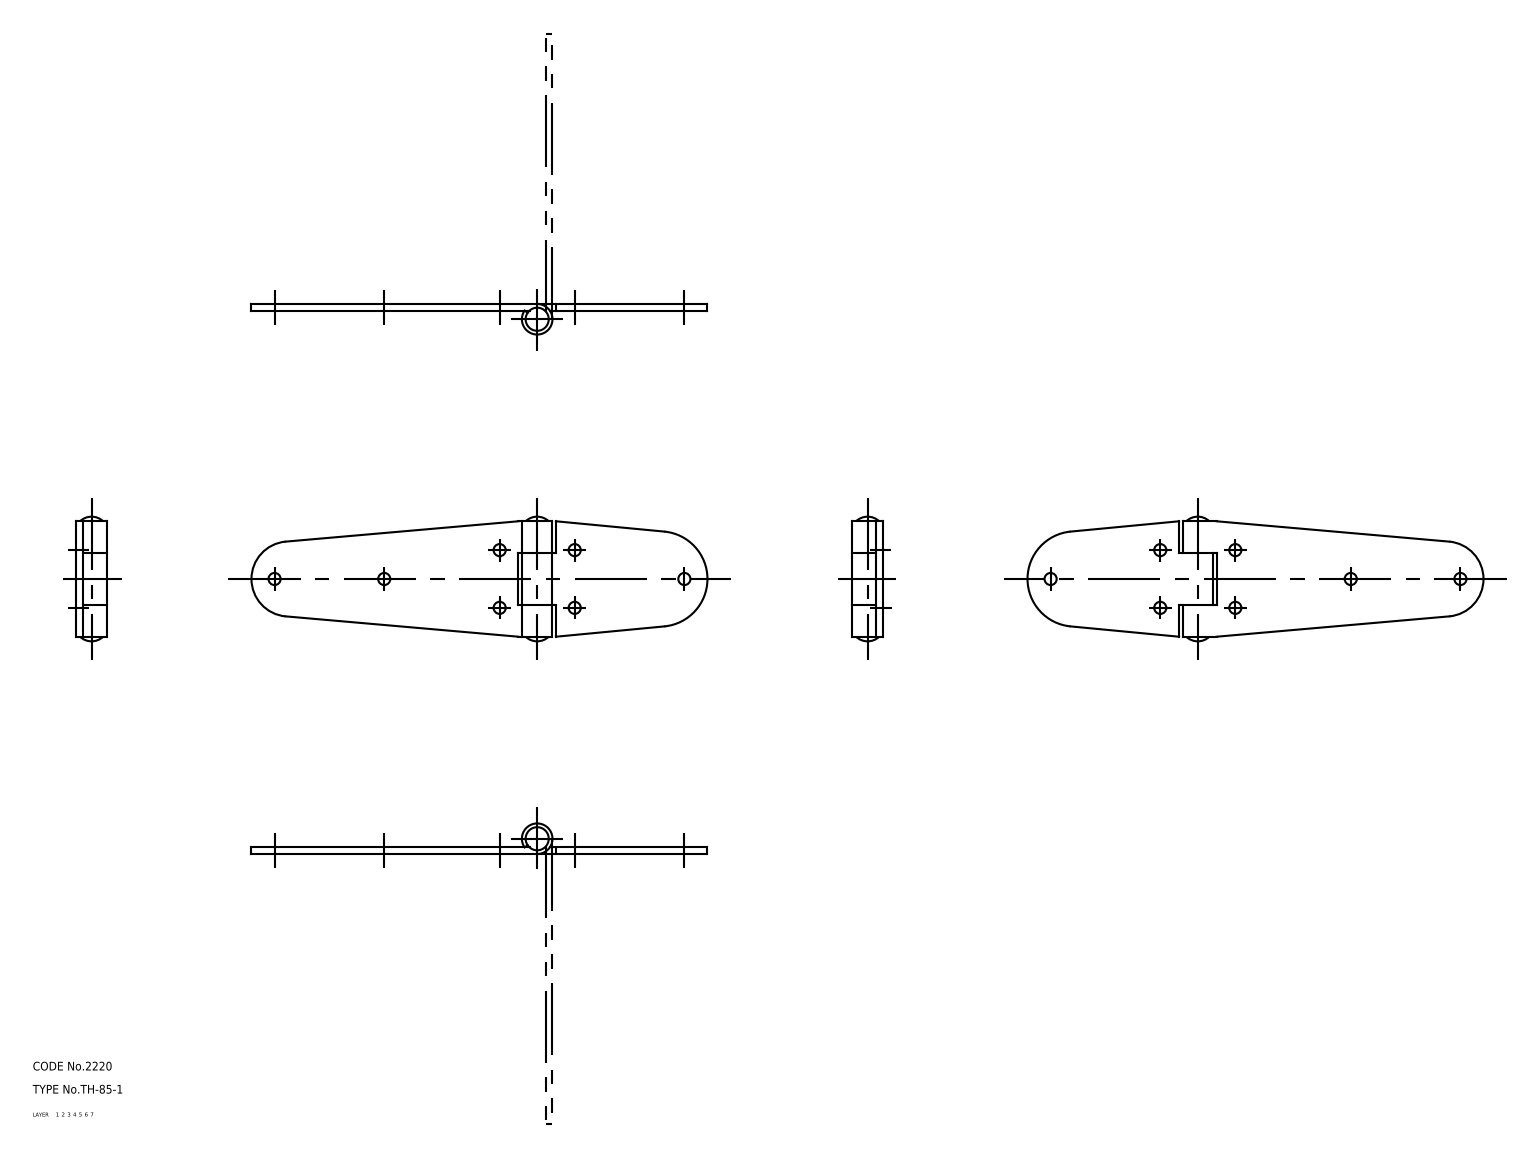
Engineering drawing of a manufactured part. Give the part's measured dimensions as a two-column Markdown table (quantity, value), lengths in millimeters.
| quantity | value |
| --- | --- |
| part name | hinge piece_B; hinge piece_A; shaft; TH_85_1_18205_36 |
| STEP written by | CADfix (AUTOMOTIVE_DESIGN) |
| units | millimeters |
| bodies | 3 solids, 48 faces (0 planar, 0 cylindrical, 48 other) |
| overall size | 158 × 43.2 × 10.6 |
| volume | 14 283 mm³ |
| surface area | 13 813 mm² |
